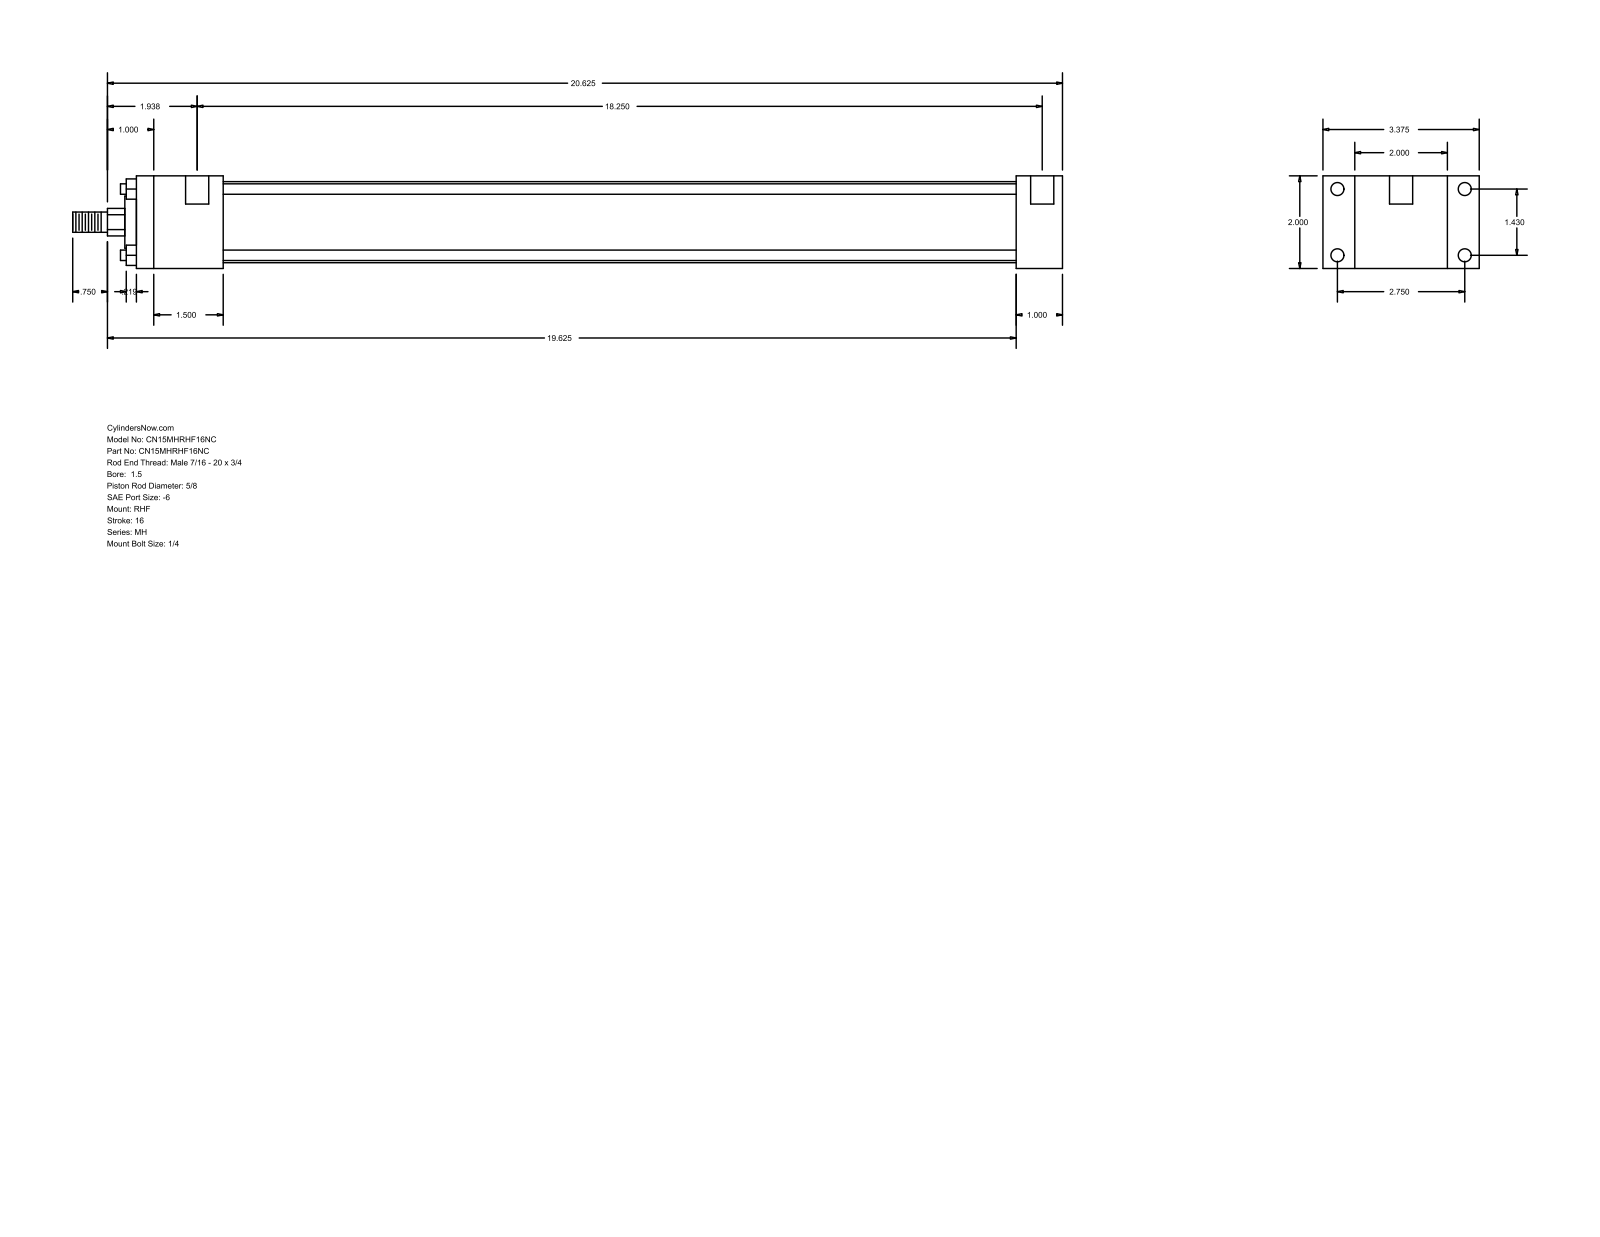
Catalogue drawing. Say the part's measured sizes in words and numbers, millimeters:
The part is named "MH_RHF__0150_0.625". Its 3-D file was written by "GSSL Pune (CONFIG_CONTROL_DESIGN)". It is 0 solids with 88 faces: 60 planar, 28 cylindrical and 0 other. Overall it measures 542.92 by 85.72 by 50.8 millimeters. Round holes: 4 of diameter 5.56, 4 of diameter 7.14, 2 of diameter 12.7. Round bosses or shafts: 4 of diameter 5.71, 1 of diameter 44.45, 1 of diameter 28.57, 1 of diameter 15.88, 1 of diameter 11.11. Partial cylindrical surfaces (rounded edges, fillets, slot ends): 1 of radius 7.54. The main face-to-face distances are 50.8, 25.4, 17.46, 68.26, 482.6, 508, 85.72, 47.62, 434.98, 460.38. The hole center spacings are 36.32, 69.84, 78.72, 466.72, 3.17, 463.55.
